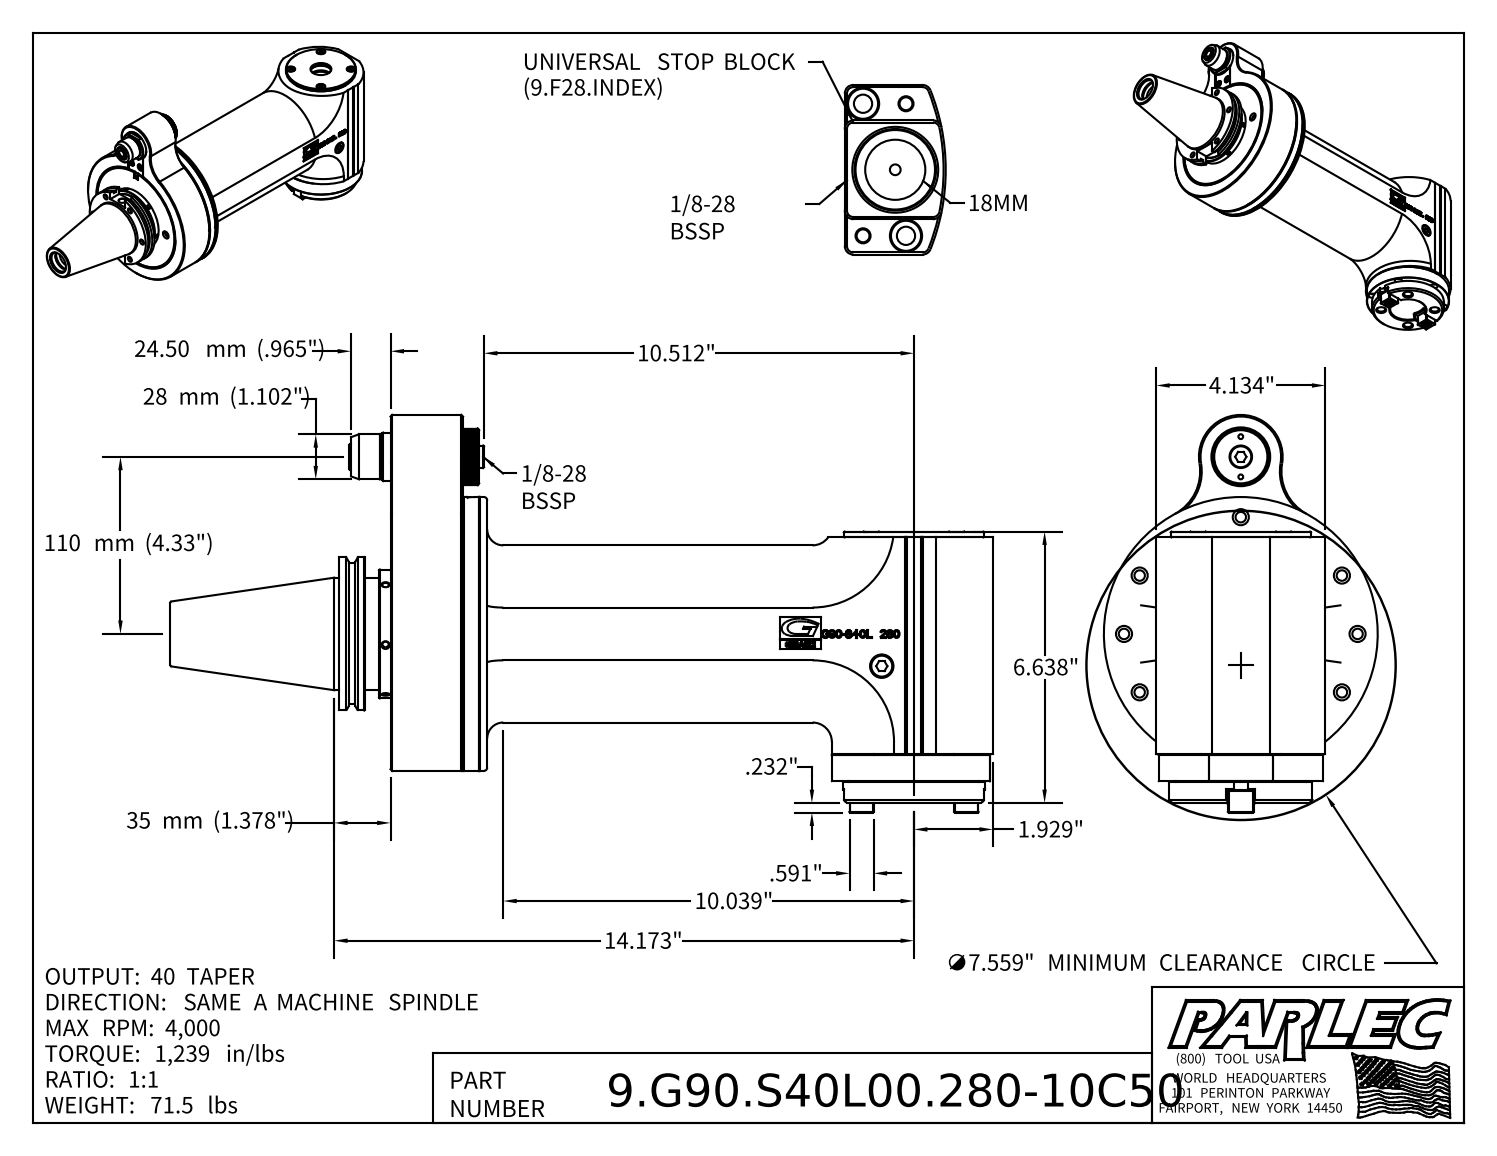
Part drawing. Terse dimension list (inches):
name: 9.G90.S40L00.280-10C50; 9_G90_S40L0_280; 9_GA4_451_1 (Classic, Type 4, Cat50, 110mm, 28x24.5P)
written by: Autodesk Inventor 2022 (AUTOMOTIVE_DESIGN)
unit: in
bodies: 22 solids, 2113 faces (1149 planar, 443 cylindrical, 521 other)
size: 20.11 × 9.72 × 6.693
volume: 238.6 in³; area: 947 in²
holes: 22× ⌀0.165, 13× ⌀0.256, 13× ⌀0.394, 10× ⌀0.13, 6× ⌀0.217, 6× ⌀0.354, 5× ⌀0.197, 5× ⌀0.335, 4× ⌀0.276, 2× ⌀0.118, 2× ⌀0.205, 2× ⌀0.362
bosses: 4× ⌀0.386, 2× ⌀1.378, 2× ⌀0.551, 2× ⌀0.504, 2× ⌀0.394, 2× ⌀0.354, 2× ⌀0.307, 1× ⌀6.693
rounds: 16× R0.118, 12× R0.039, 8× R0.079, 6× R0.392, 2× R0.177, 2× R0.197, 2× R0.394, 2× R1.024
face distances: 1.772, 0.472, 1.299, 0.591, 4.134, 1.89, 0.63, 2.362, 0.154, 0.319
hole spacings: 2.854, 1.478, 1.811, 4.037, 4.944, 5.514, 1.941, 1.071
